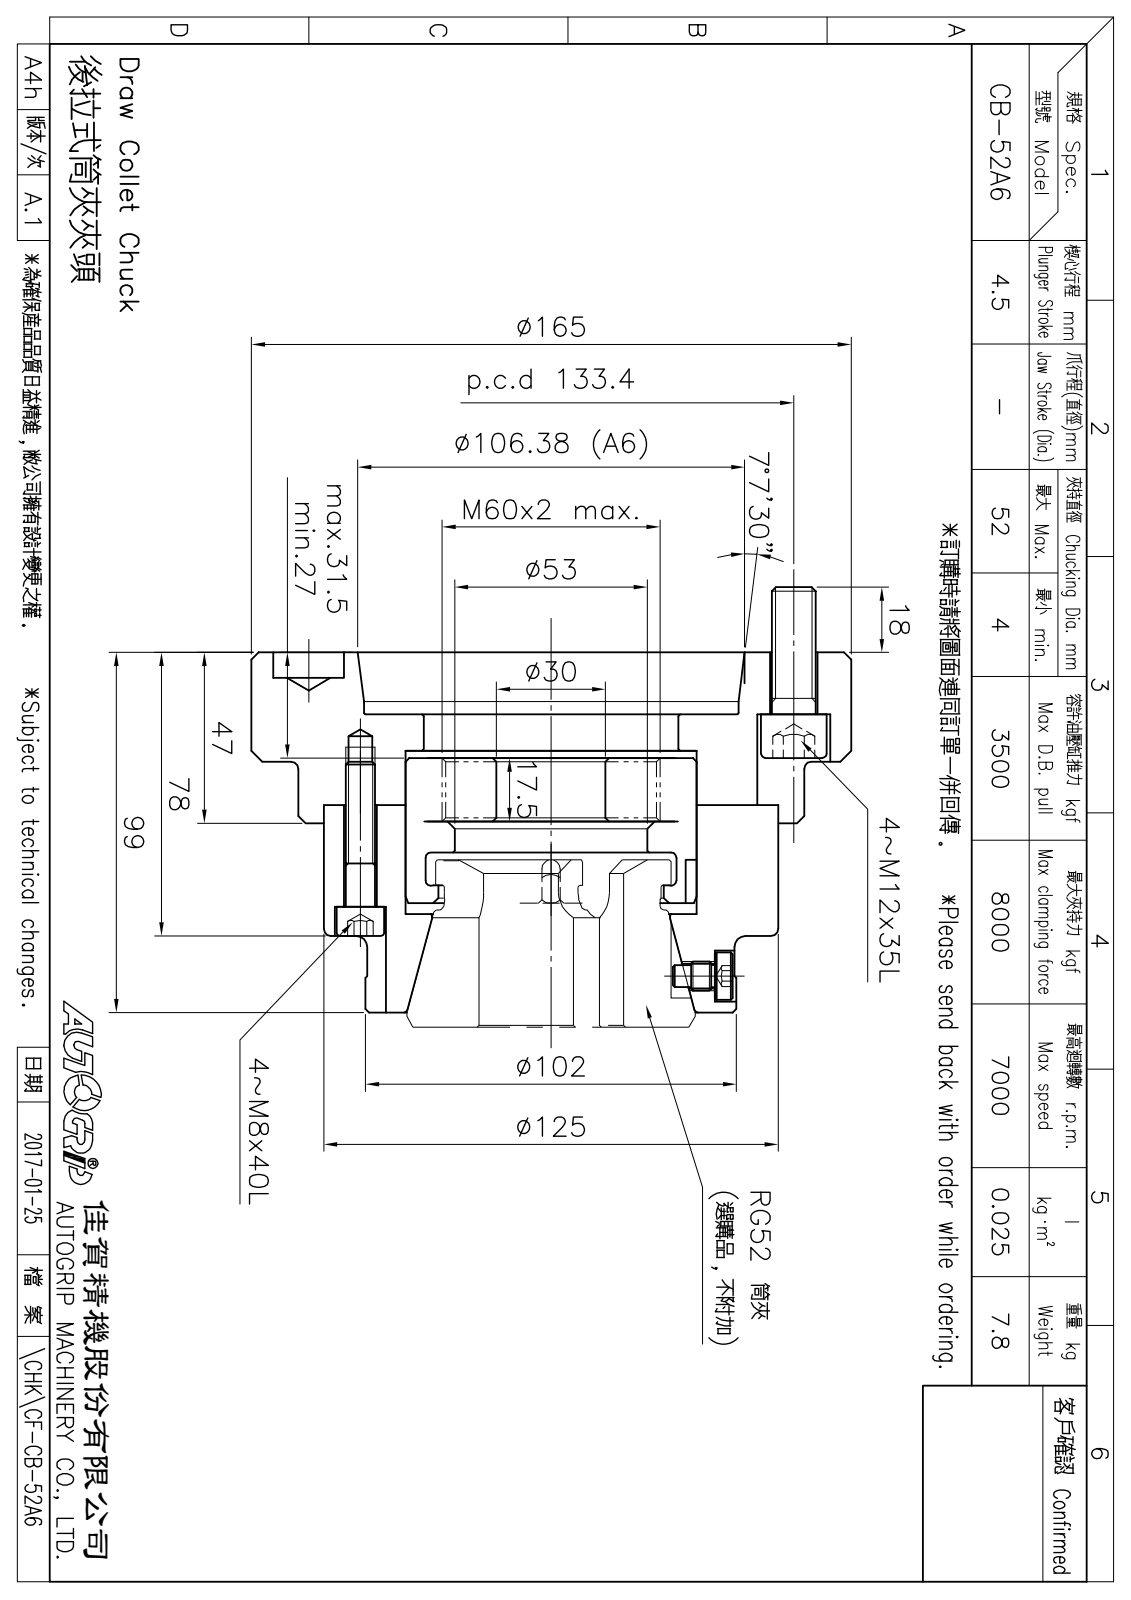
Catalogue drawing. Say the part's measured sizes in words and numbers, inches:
The part is named "圓頭內六角螺栓_M12x35; CF-CB-52-02000; 圓頭內六角螺栓_M8x40; CF-CB-52-01000 (+2 more)". Its 3-D file was written by "SolidWorks 2016 (CONFIG_CONTROL_DESIGN)". It is 11 solids with 385 faces: 148 planar, 118 cylindrical and 119 other. Overall it measures 6.496 by 6.496 by 4.606 inches. Its volume is 62.24 cubic inches and its surface area 269.3 square inches. Round holes: 4 of diameter 0.268, 4 of diameter 0.354, 4 of diameter 0.512, 4 of diameter 0.551, 4 of diameter 0.787, 2 of diameter 0.768, 1 of diameter 1.181, 1 of diameter 2.087, 1 of diameter 2.441, 1 of diameter 2.579, 1 of diameter 2.717, 1 of diameter 2.756. Round bosses or shafts: 4 of diameter 0.709, 4 of diameter 0.512, 4 of diameter 0.472, 4 of diameter 0.315, 1 of diameter 6.496, 1 of diameter 5.472, 1 of diameter 4.016, 1 of diameter 3.976. The main face-to-face distances are 1.654, 0.984, 0.669, 1.181, 1.063, 0.394, 0.591, 0.118, 0.472, 0.512. The hole center spacings are 1.868, 4.337, 2.063, 2.626, 2.917, 3.714, 0.826, 1.358.
